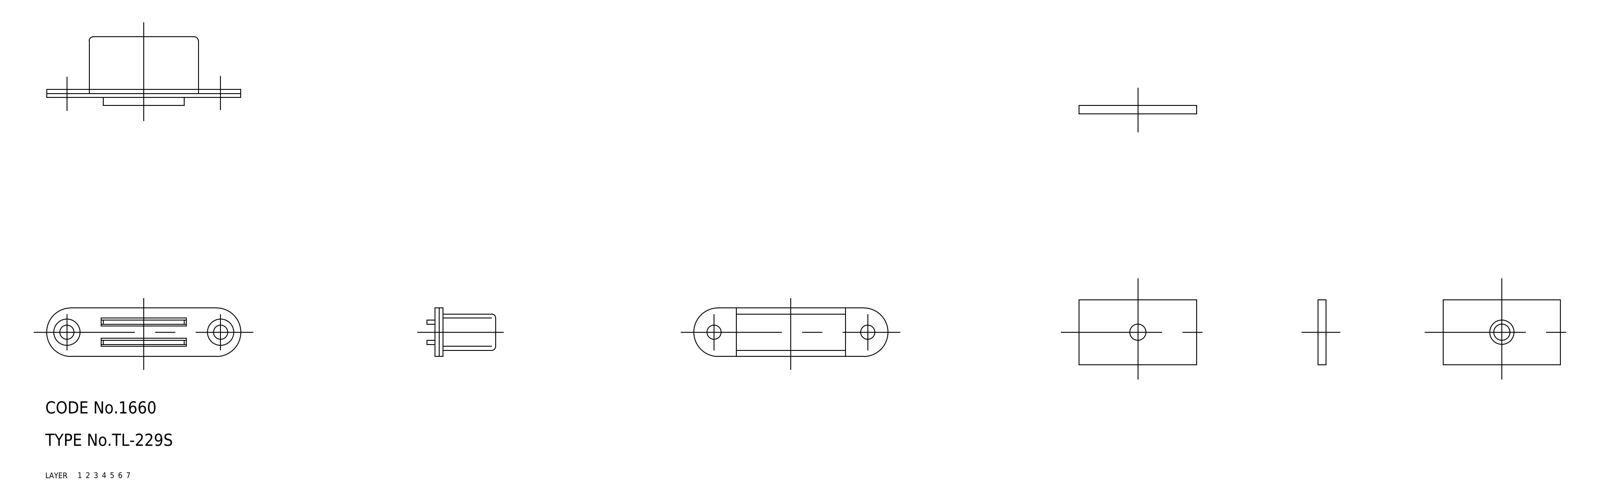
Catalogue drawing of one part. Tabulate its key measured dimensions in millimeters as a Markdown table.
| quantity | value |
| --- | --- |
| part name | 67113105; 67113118; 67113131; 67113144 (+1 more) |
| STEP written by | CADfix (AUTOMOTIVE_DESIGN) |
| units | millimeters |
| bodies | 5 solids, 96 faces (0 planar, 0 cylindrical, 96 other) |
| overall size | 48 × 34.05 × 16 |
| volume | 3 336 mm³ |
| surface area | 6 655 mm² |
